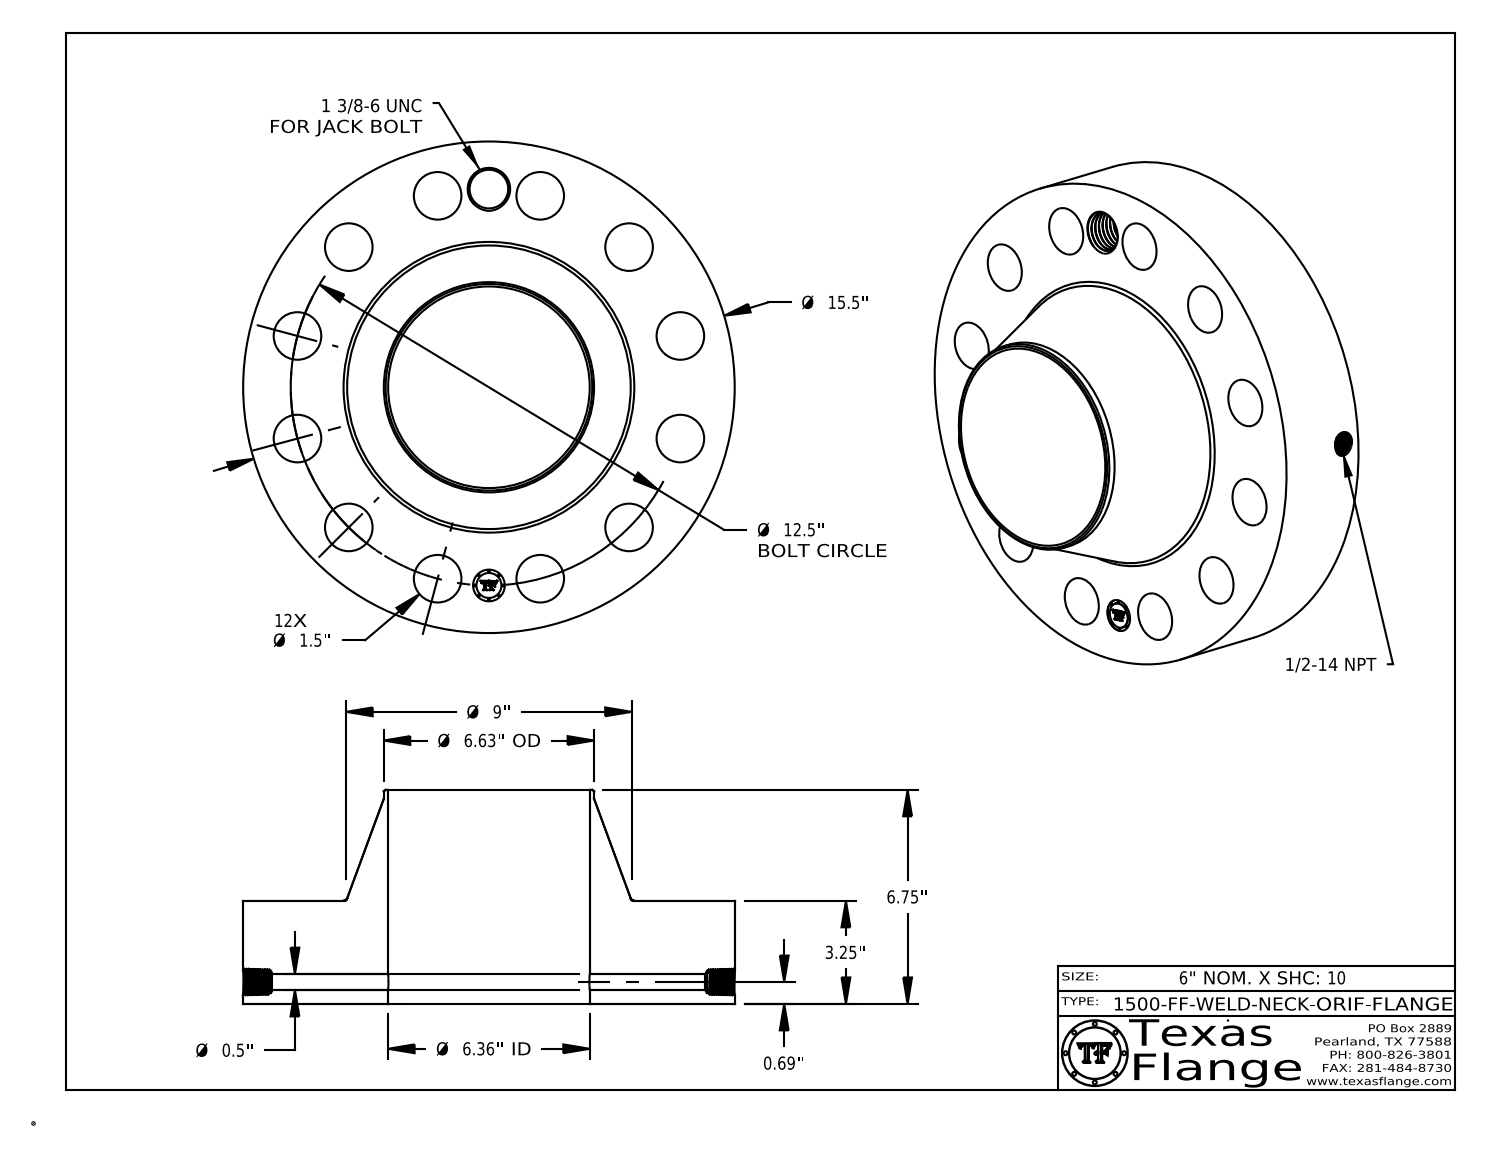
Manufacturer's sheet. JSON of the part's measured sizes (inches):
{"part_name": "1500-FF-WELD-NECK", "step_written_by": "CATIA V5 STEP AP214 (AUTOMOTIVE_DESIGN)", "units": "inches", "bodies": {"solids": 1, "faces": 801, "planar": 368, "cylindrical": 109, "other": 324}, "overall_size": [15.5, 15.5, 6.75], "volume_in3": 488.9, "surface_area_in2": 841.5, "round_holes": [[1.5, 12], [0.5, 1], [0.672, 1], [1, 1], [1.219, 1], [6.357, 1]], "round_bosses_or_shafts": [[0.061, 8], [15.5, 1], [6.63, 1], [0.788, 1]], "face_to_face_distances": [3.25, 6.75, 3.5, 3.235, 0.015, 3.515, 0.298, 0.293, 0.054, 0.248], "hole_center_spacings": [6.25, 12.074, 3.235, 8.839, 10.825, 12.5, 1.631, 3.235]}
